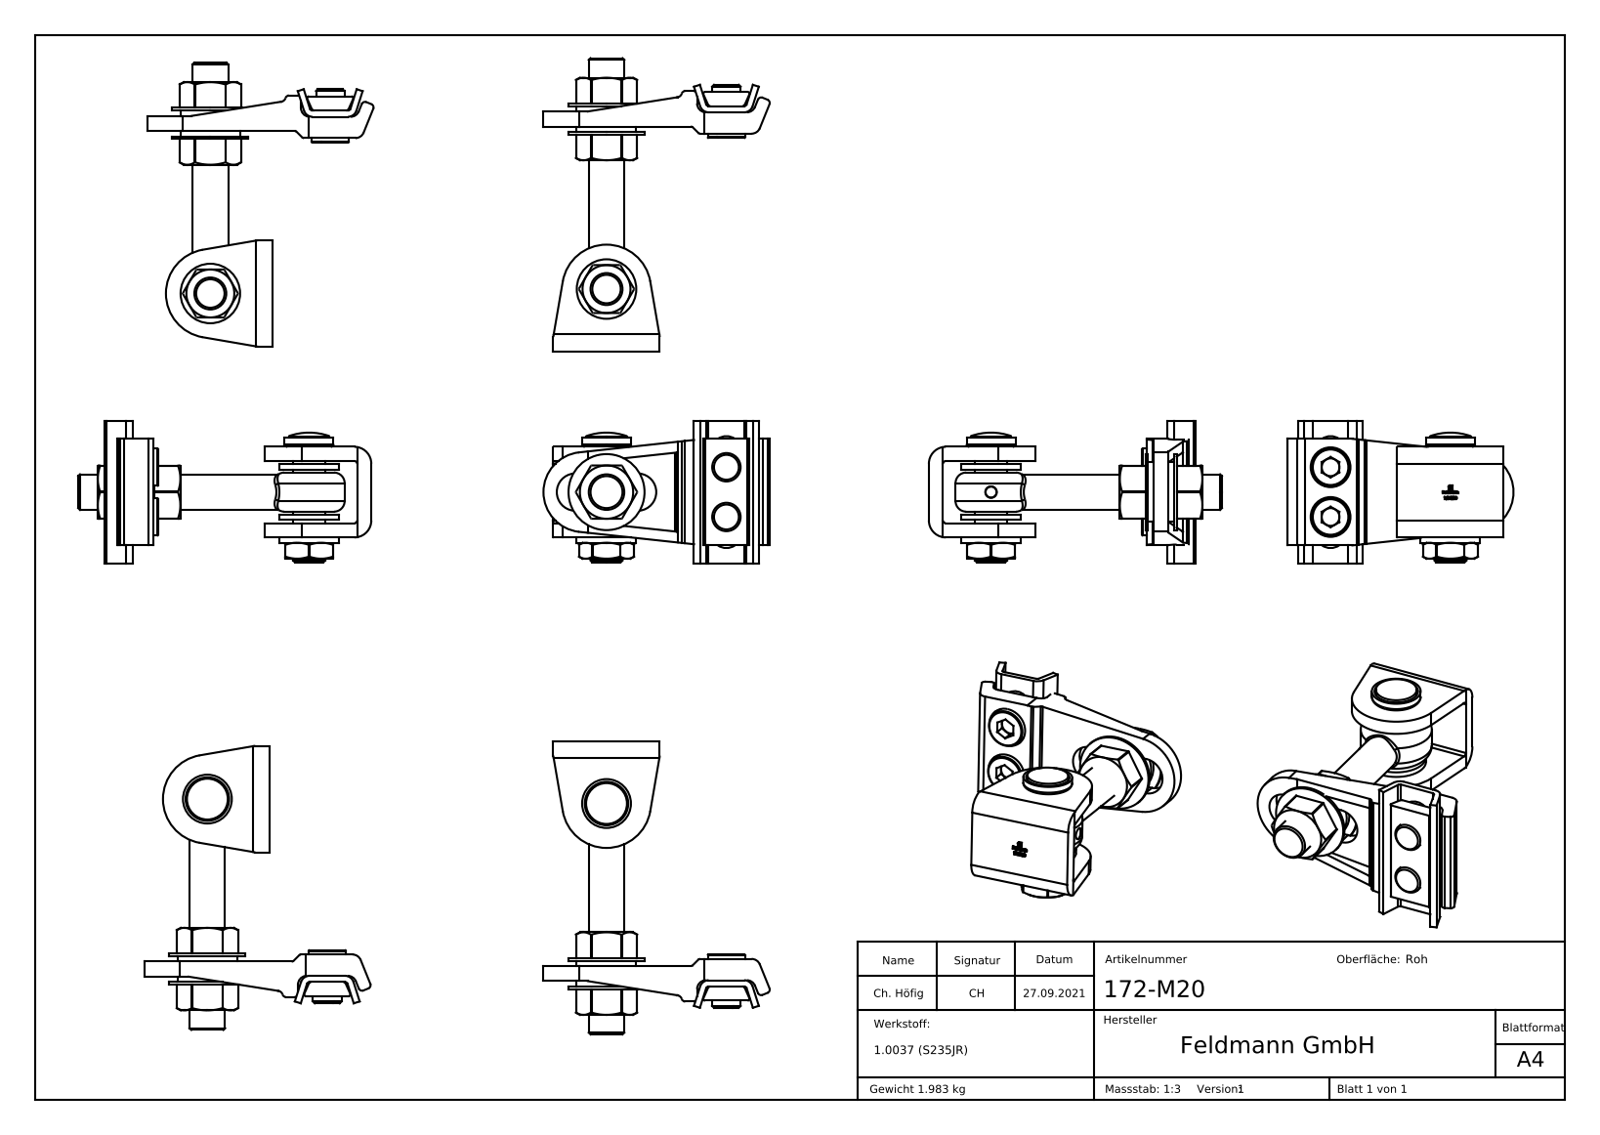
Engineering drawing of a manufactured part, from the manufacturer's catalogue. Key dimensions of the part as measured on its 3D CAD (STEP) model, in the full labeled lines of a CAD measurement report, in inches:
Part name (STEP PRODUCT): 172-M20; 172-Mxx Teil4_172-M20 Teil4; 172-Mxx Teil2_172-M20 Teil2; DIN 936 M8-M24_DIN 936 M18 Stahl (+8 more)
STEP written by: SolidWorks 2018 (CONFIG_CONTROL_DESIGN)
Units: inches
Bodies: 17 solids, 500 faces (264 planar, 85 cylindrical, 151 other)
Overall size (bounding box): 6.496 × 5.016 × 3.15
Volume: 15.49 in³ · Surface area: 142.8 in²
Round holes (diameter × count): ⌀0.748 ×3, ⌀0.244 ×2, ⌀0.551 ×2, ⌀0.756 ×2, ⌀0.882 ×2, ⌀0.61 ×1, ⌀0.689 ×1, ⌀0.728 ×1, ⌀0.965 ×1
Round bosses / shafts (diameter × count): ⌀1.319 ×2, ⌀0.827 ×2, ⌀0.63 ×2, ⌀1.685 ×1, ⌀1.575 ×1, ⌀1.083 ×1, ⌀0.906 ×1, ⌀0.787 ×1
Partial cylindrical surfaces — rounded edges, fillets, slot ends (radius × count): R0.02 ×12, R0.059 ×8, R0.197 ×5, R0.079 ×4, R0.039 ×2, R0.335 ×2, R0.374 ×2, R0.413 ×2
Main face-to-face distances: 0.315, 0.118, 0.453, 1.693, 0.138, 0.433, 0.571, 4.98, 0.492, 0.177
Hole centre spacings: 2.714, 0.02, 1.102, 2.71, 2.718
